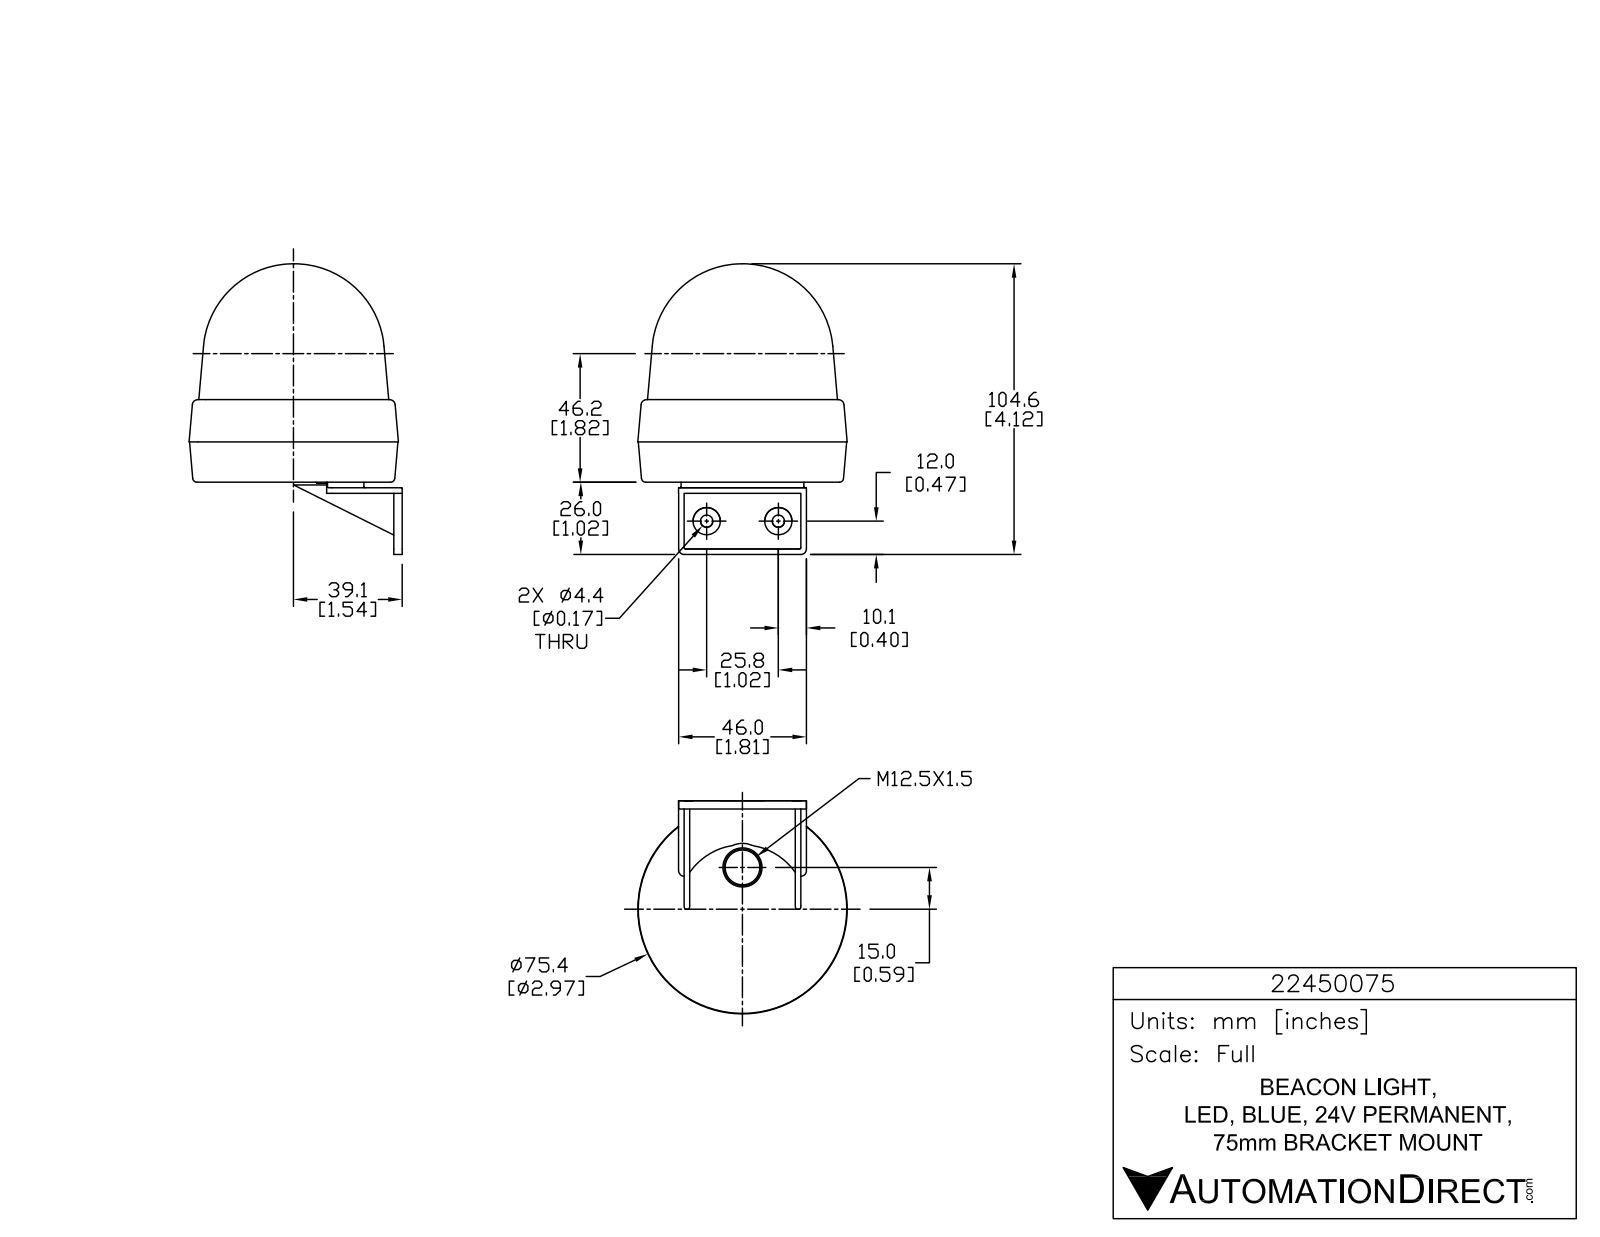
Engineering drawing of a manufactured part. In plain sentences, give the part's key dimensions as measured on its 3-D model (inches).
The part is named "22450075". Its 3-D file was written by "SolidWorks 2015 (AUTOMOTIVE_DESIGN)". It is 1 solid with 819 faces: 549 planar, 180 cylindrical and 90 other. Overall it measures 4.117 by 3.253 by 2.967 inches. Its volume is 16.02 cubic inches and its surface area 41.97 square inches. Round holes: 3 of diameter 0.059, 2 of diameter 0.173. Round bosses or shafts: 3 of diameter 0.339, 3 of diameter 0.084, 2 of diameter 0.386. Partial cylindrical surfaces (rounded edges, fillets, slot ends): 9 of radius 0.005, 6 of radius 0.005, 6 of radius 0.012, 6 of radius 0.012, 6 of radius 0.012, 6 of radius 0.02, 6 of radius 0.196, 4 of radius 0.079. The main face-to-face distances are 0.079, 0.157, 1.574, 0.039, 0.118, 1.653, 1.496, 0.079, 1.654, 1.732. The hole center spacings are 1.016.
